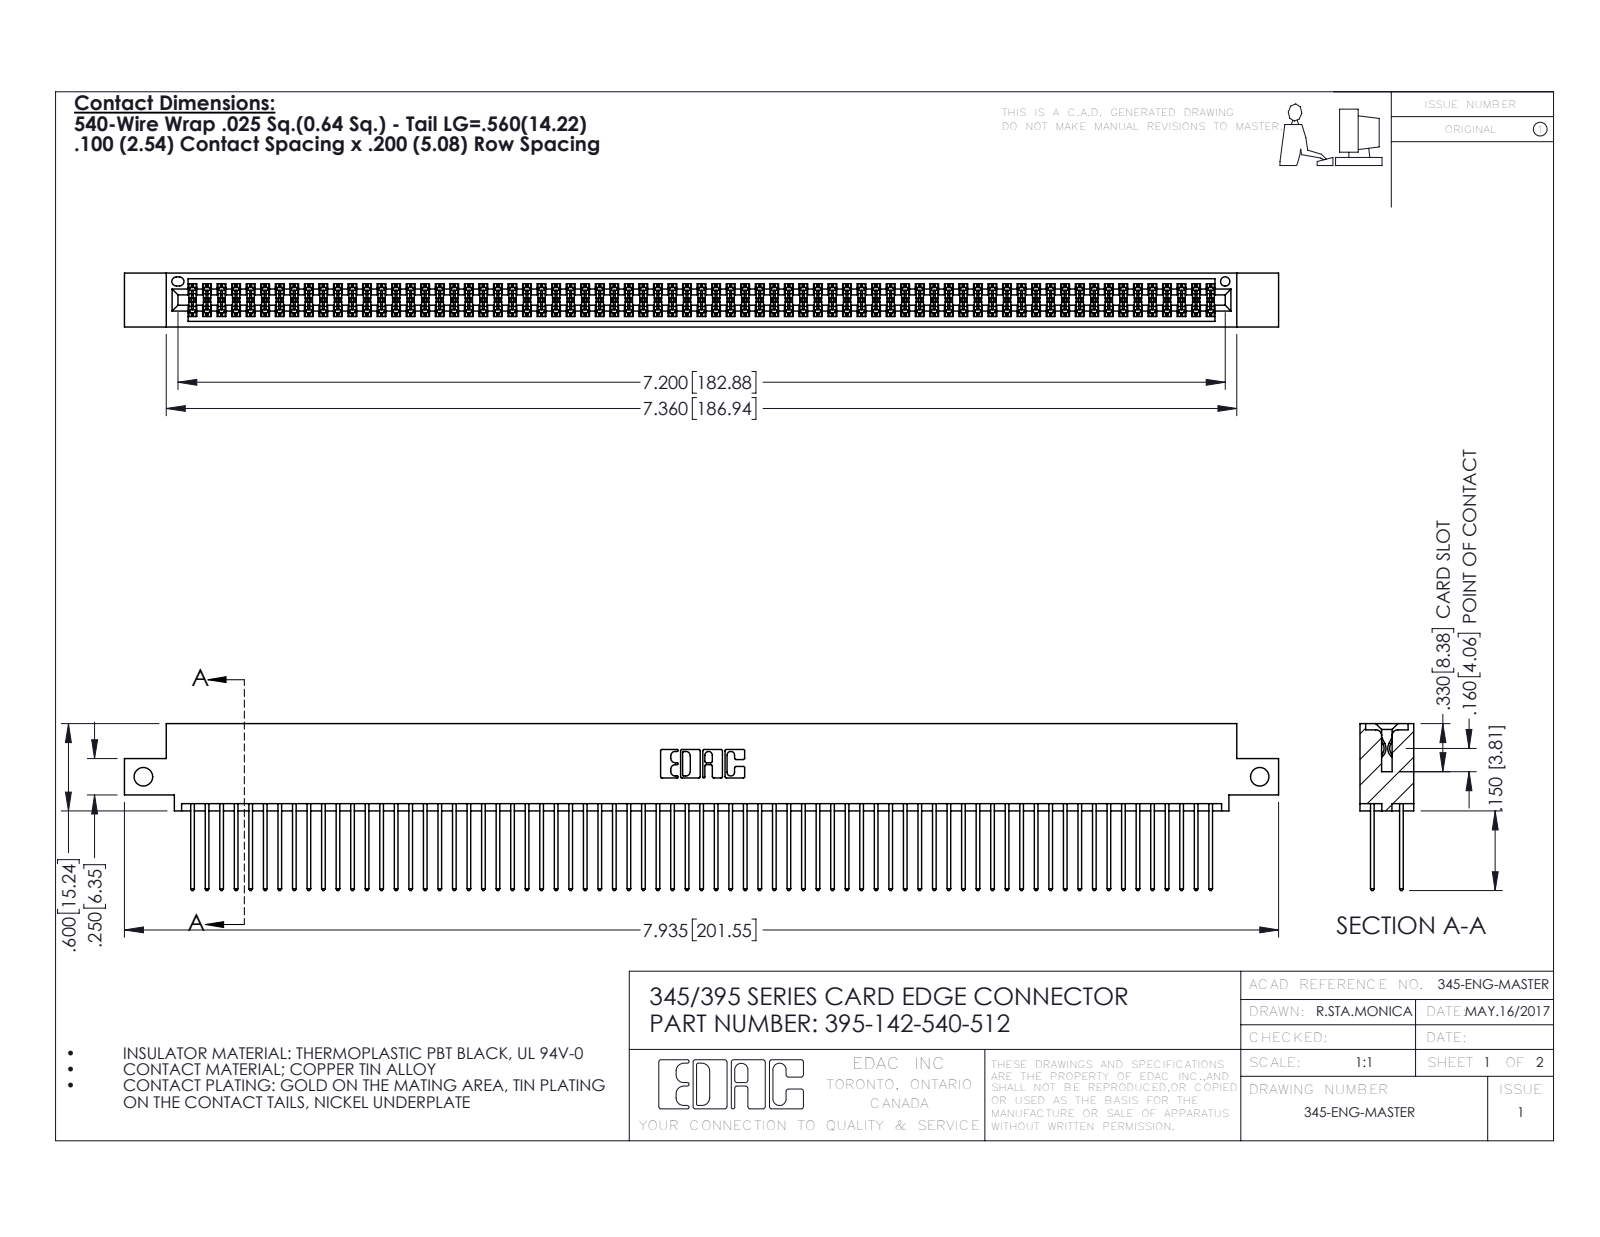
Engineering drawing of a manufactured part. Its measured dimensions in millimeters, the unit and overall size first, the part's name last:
Units: millimetres
Overall size (bounding box): 201.5 × 29.1 × 9.4
Round holes (diameter × count): ⌀3.3 ×2, ⌀1.6 ×1
Partial cylindrical surfaces — rounded edges, fillets, slot ends (radius × count): R0.2 ×213, R0.3 ×142, R0.3 ×22, R0.2 ×6, R0.8 ×6, R0.7 ×3, R0.4 ×2, R0.5 ×2
Main face-to-face distances: 7.6, 1.8, 5.1, 2.5, 6.9, 0.6, 5.7, 9.4, 4.4, 3.8
Hole centre spacings: 194.9
Volume: 20 220 mm³ · Surface area: 32 920 mm²
Bodies: 143 solids, 7230 faces (4770 planar, 2460 cylindrical, 0 other)
Part name (STEP PRODUCT): 395-142-540-512; 345-292-001_345-293-140; 345 Part_0.110 Offset - Side Mount
STEP written by: SolidWorks 2016 (CONFIG_CONTROL_DESIGN)
